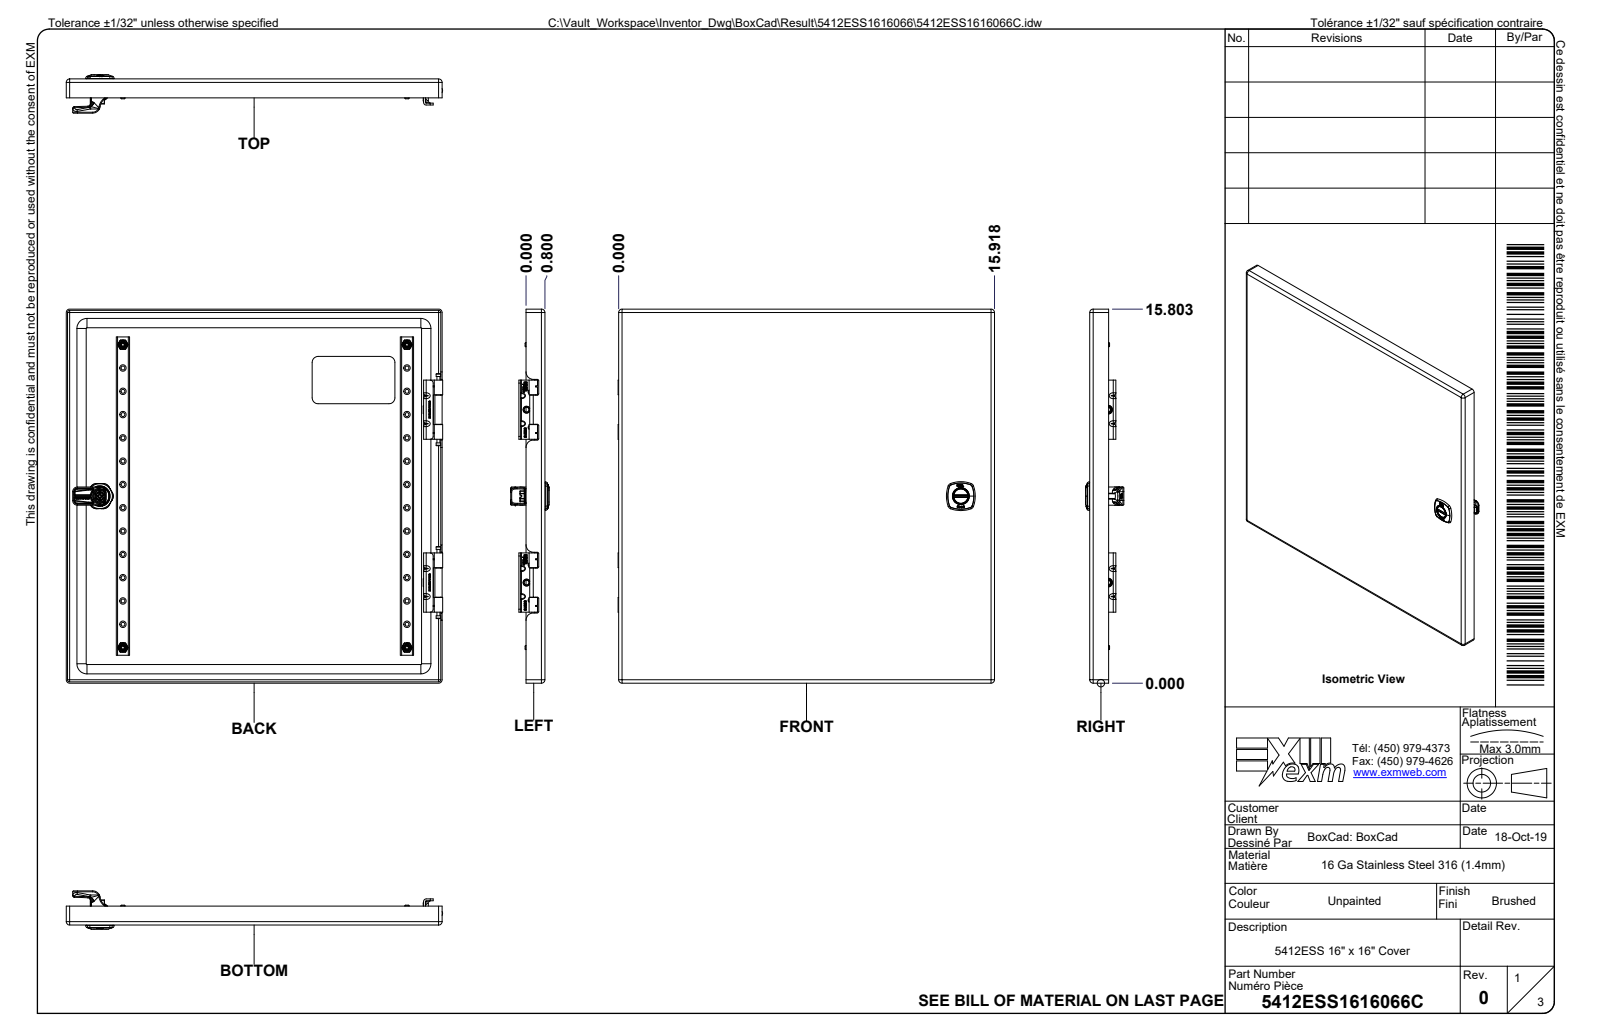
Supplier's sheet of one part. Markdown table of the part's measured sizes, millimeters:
| quantity | value |
| --- | --- |
| part name | 5412ESS1616066; 5412ESS1616066B; 5412ESS1616066B-P; STK-Q-16020 (+8 more) |
| STEP written by | Autodesk Inventor 2024 (AUTOMOTIVE_DESIGN) |
| units | millimeters |
| bodies | 56 solids, 7557 faces (2187 planar, 1702 cylindrical, 3668 other) |
| overall size | 406.4 × 406.4 × 185.6 |
| volume | 1 374 000 mm³ |
| surface area | 1 748 000 mm² |
| round holes (diameter × count) | 4.2 × 24, 0.8 × 9, 8 × 8, 5.1 × 7, 7.4 × 6, 7.9 × 5, 1.1 × 4, 5 × 4, 6.8 × 4, 6.9 × 4, 9.9 × 4, 6 × 2 |
| round bosses / shafts (diameter × count) | 6 × 24, 0.8 × 9, 5.9 × 8, 1 × 8, 18.2 × 4, 9.5 × 4, 7.9 × 4, 6.7 × 4 |
| partial cylindrical surfaces (radius × count) | 0.5 × 78, 1 × 58, 0.2 × 54, 0.8 × 26, 2.1 × 24, 0.3 × 18, 0.3 × 16, 3.2 × 16 |
| main face-to-face distances | 1.3, 179.9, 405.1, 178.5, 181.2, 23.5, 22.2, 156.3, 157.7, 2.7 |
| hole center spacings | 25, 50, 75, 306.6, 100, 309.7, 314.7, 125 |
